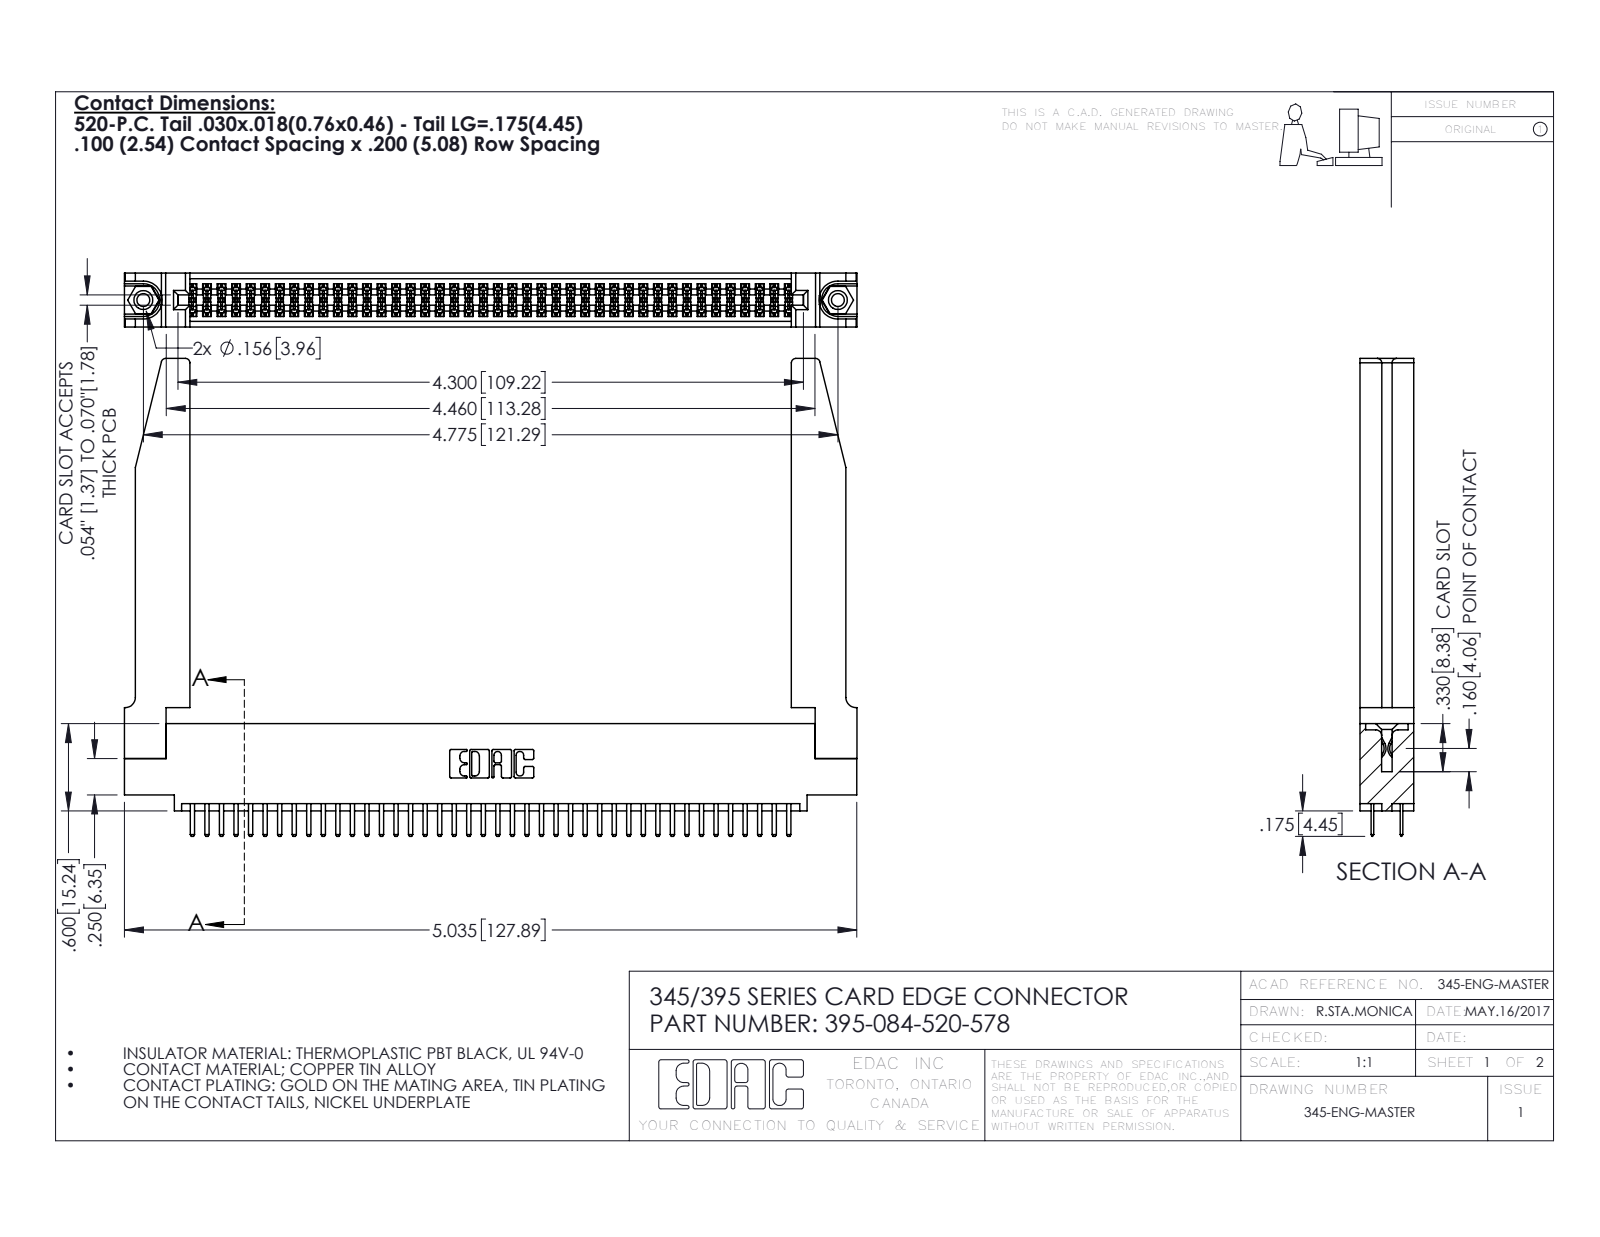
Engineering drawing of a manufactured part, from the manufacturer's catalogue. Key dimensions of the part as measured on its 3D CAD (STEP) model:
Part name (STEP PRODUCT): 395-084-520-578; 345 Part_0.110 Offset - 0.156 Dia-TH; 345-250-001_345-250-001-102; 345-292-001_345-293-120 (+1 more)
STEP written by: SolidWorks 2016 (CONFIG_CONTROL_DESIGN)
Units: inches
Bodies: 89 solids, 4900 faces (3166 planar, 1682 cylindrical, 52 other)
Overall size (bounding box): 5.036 × 3.285 × 0.37
Volume: 1.226 in³ · Surface area: 38.84 in²
Round holes (diameter × count): ⌀0.089 ×2, ⌀0.125 ×2, ⌀0.156 ×2, ⌀0.064 ×1
Round bosses / shafts (diameter × count): ⌀0.155 ×2
Partial cylindrical surfaces — rounded edges, fillets, slot ends (radius × count): R0.006 ×126, R0.01 ×88, R0.01 ×22, R0.03 ×8, R0.007 ×6, R0.031 ×6, R0.026 ×3, R0.014 ×2
Main face-to-face distances: 0.37, 0.072, 0.298, 0.2, 0.098, 0.272, 0.025, 0.225, 0.022, 0.175
Hole centre spacings: 0.27, 4.539, 4.775
